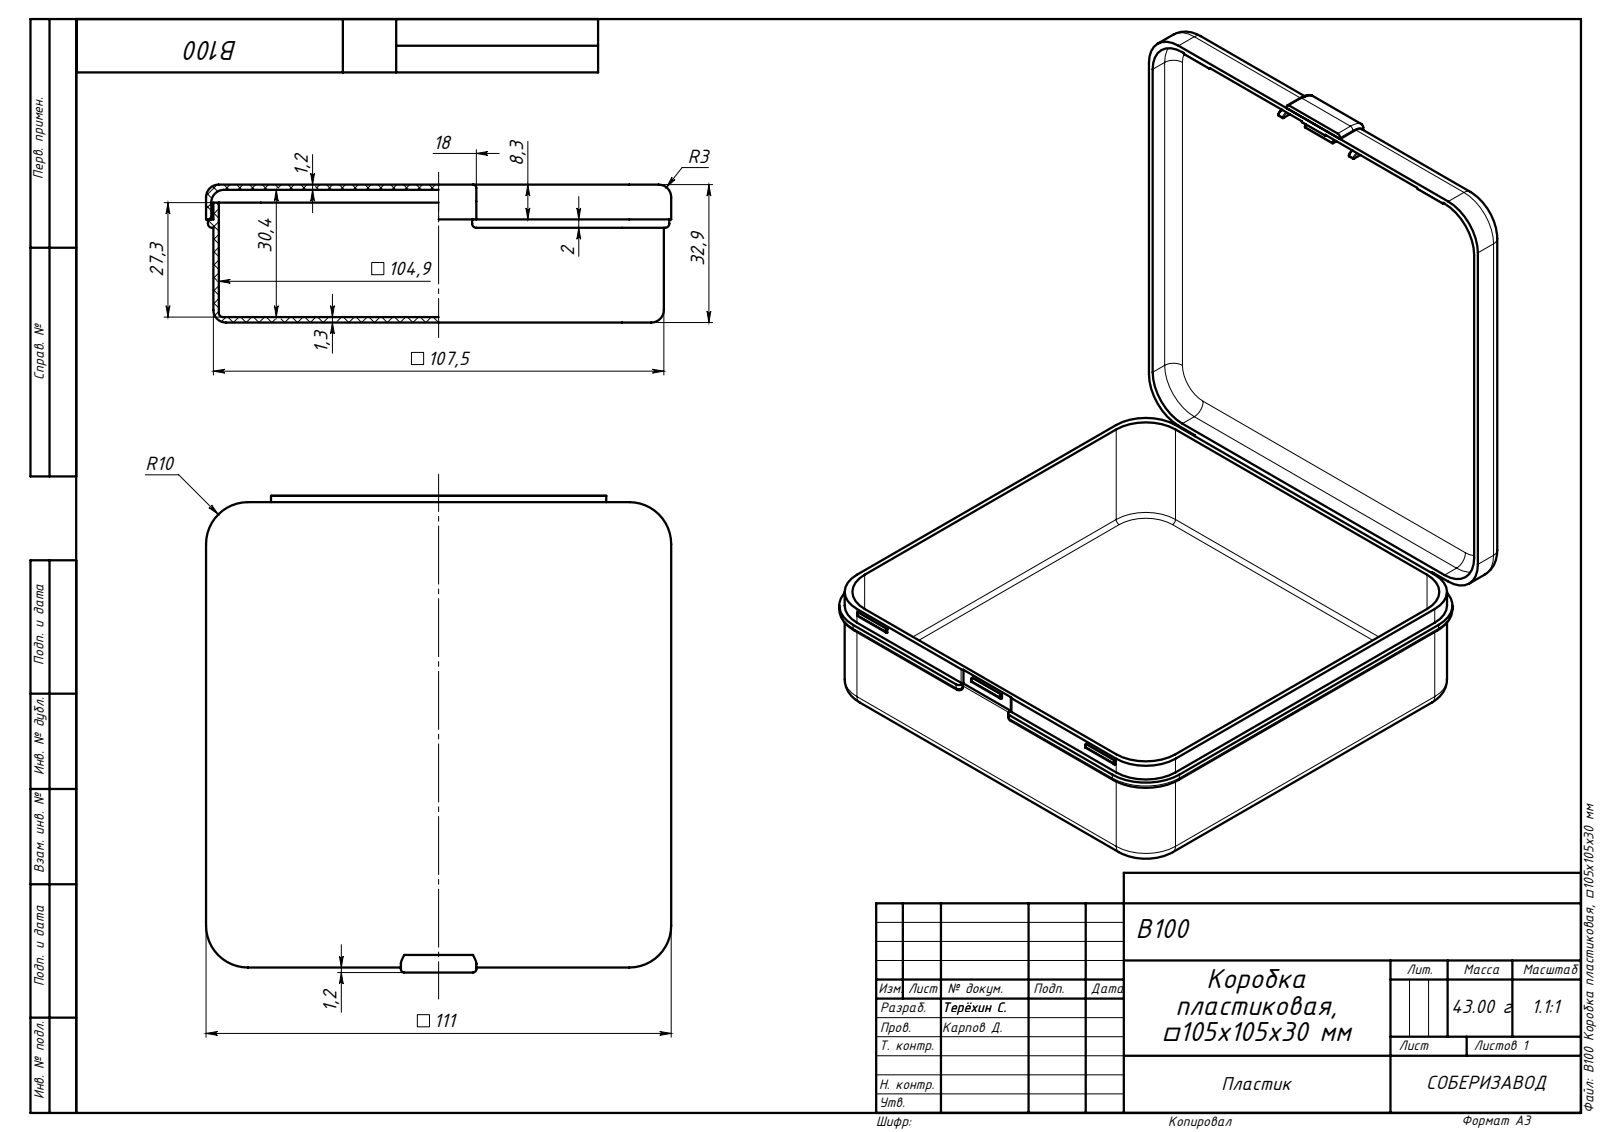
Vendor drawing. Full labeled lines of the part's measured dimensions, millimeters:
Part name (STEP PRODUCT): B100 Коробка пластиковая, ?105x105x30 мм; B100 Емкость_00; B100 Крышка_00
STEP written by: SolidWorks 2019 (AUTOMOTIVE_DESIGN)
Units: millimetres
Bodies: 3 solids, 229 faces (83 planar, 106 cylindrical, 40 other)
Overall size (bounding box): 113.7 × 111 × 32.9
Volume: 49 773 mm³ · Surface area: 76 766 mm²
Partial cylindrical surfaces — rounded edges, fillets, slot ends (radius × count): R0.2 ×24, R10 ×16, R0.4 ×15, R1 ×15, R3 ×12, R0.8 ×4, R11.3 ×4
Main face-to-face distances: 1.3, 1.25, 31.6, 30.35, 31.65, 32.9, 106.2, 107.5, 104.9, 3.05
